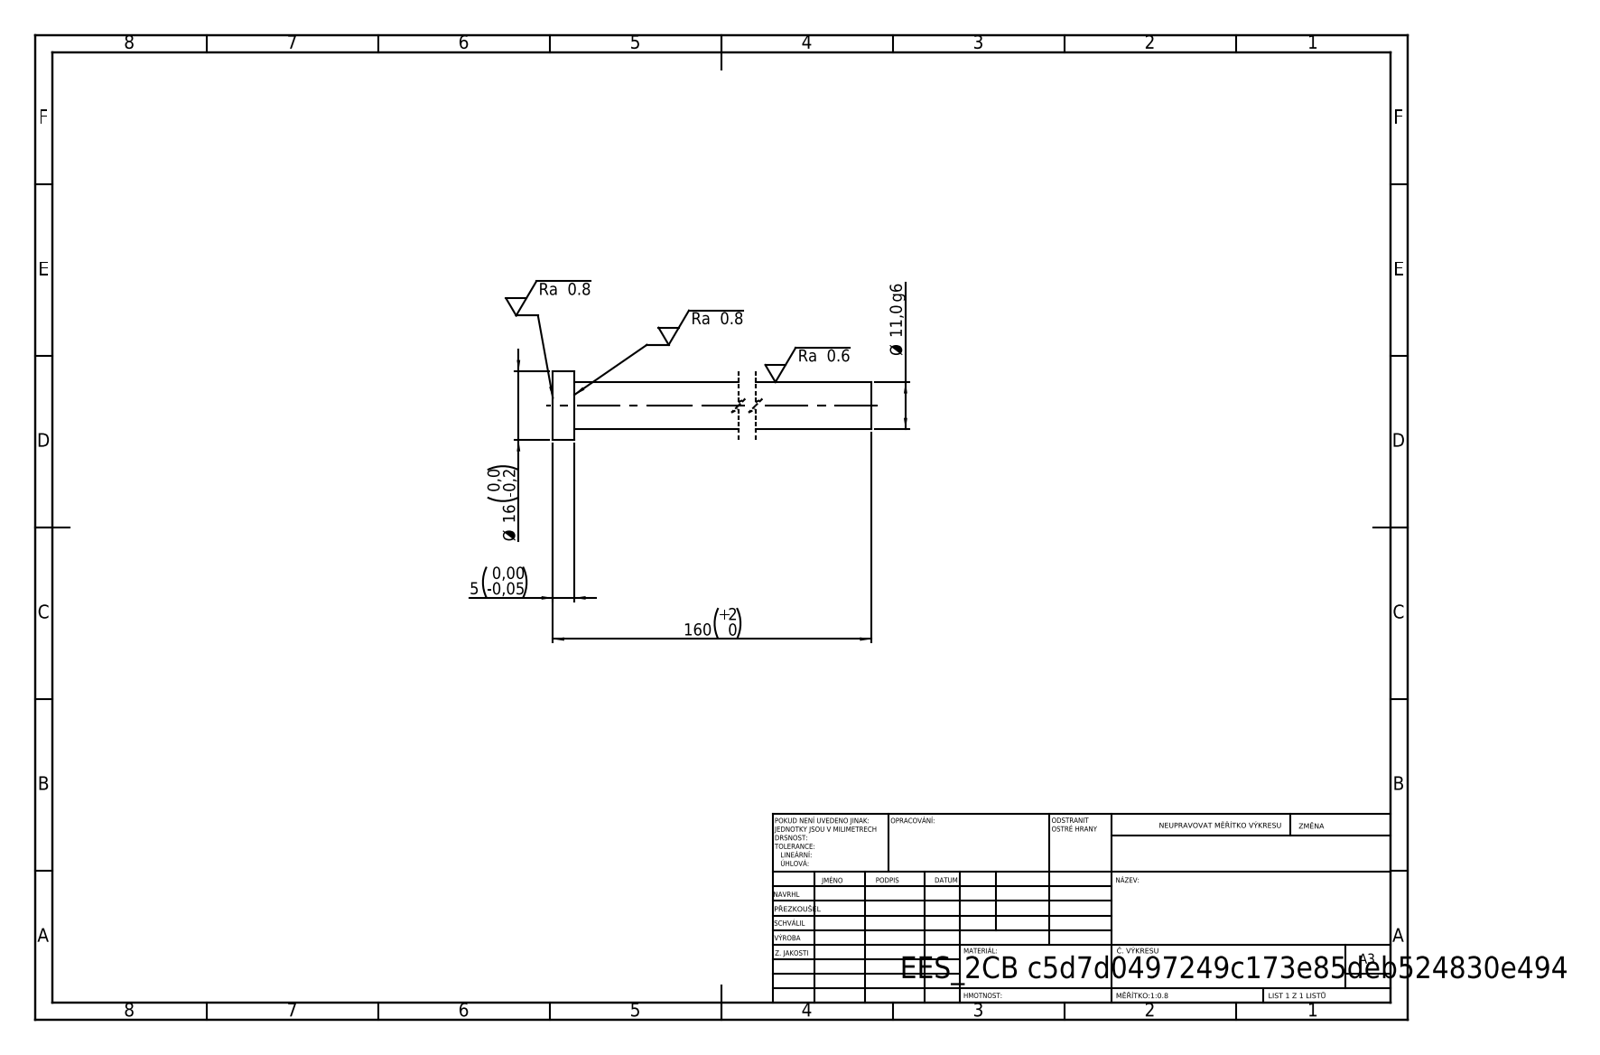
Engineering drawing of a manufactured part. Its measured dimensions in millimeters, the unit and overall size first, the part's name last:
Units: millimetres
Overall size (bounding box): 160 × 16 × 16
Round bosses / shafts (diameter × count): ⌀16 ×1, ⌀11 ×1
Main face-to-face distances: 5, 160, 155
Volume: 15 735 mm³ · Surface area: 6 010 mm²
Bodies: 1 solid, 7 faces (3 planar, 4 cylindrical, 0 other)
STEP written by: SolidWorks 2019 (CONFIG_CONTROL_DESIGN)
